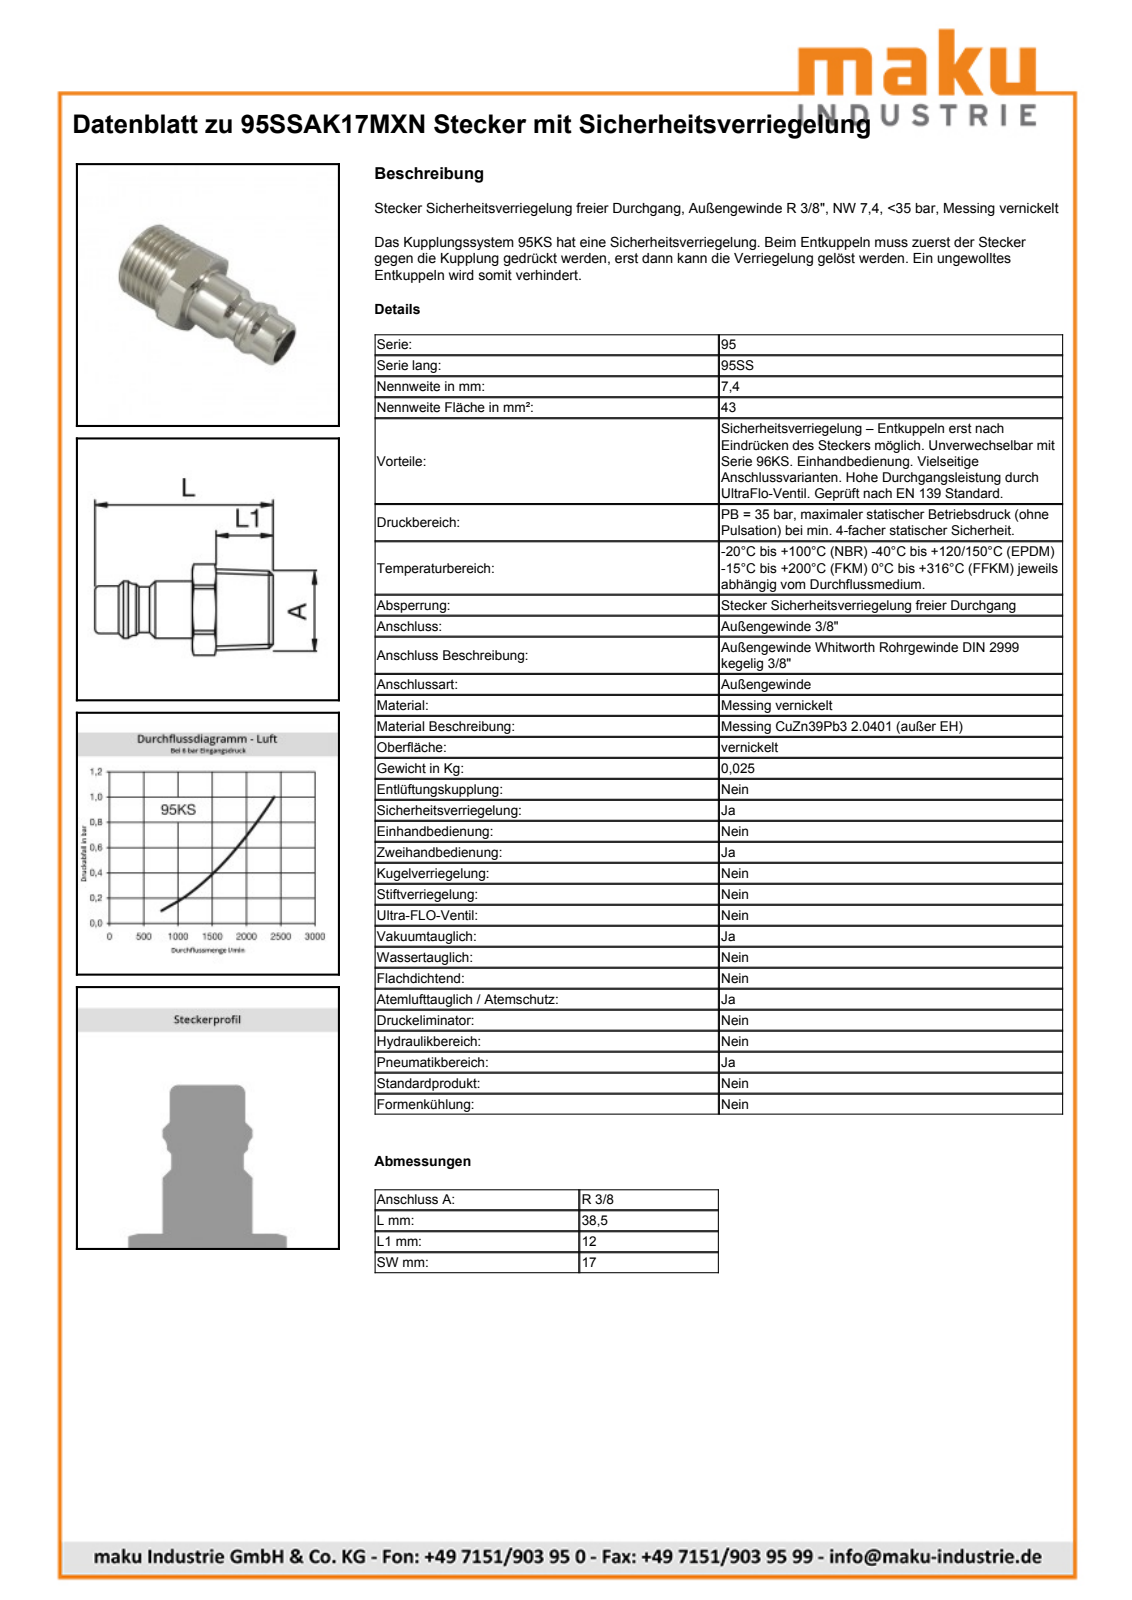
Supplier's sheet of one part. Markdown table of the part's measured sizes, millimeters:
| quantity | value |
| --- | --- |
| part name | D108836 |
| STEP written by | Autodesk Inventor 2013 (AUTOMOTIVE_DESIGN) |
| units | millimeters |
| bodies | 1 solid, 43 faces (10 planar, 13 cylindrical, 20 other) |
| overall size | 37.5 × 19.15 × 17 |
| volume | 3 252 mm³ |
| surface area | 3 010 mm² |
| round holes (diameter × count) | 7.4 × 1, 11.5 × 1 |
| round bosses / shafts (diameter × count) | 11.95 × 1, 10.8 × 1, 9.9 × 1, 9.6 × 1 |
| partial cylindrical surfaces (radius × count) | 9.57 × 1 |
| main face-to-face distances | 17, 16.9, 37.5, 20.6, 12, 4.9, 25.5 |
